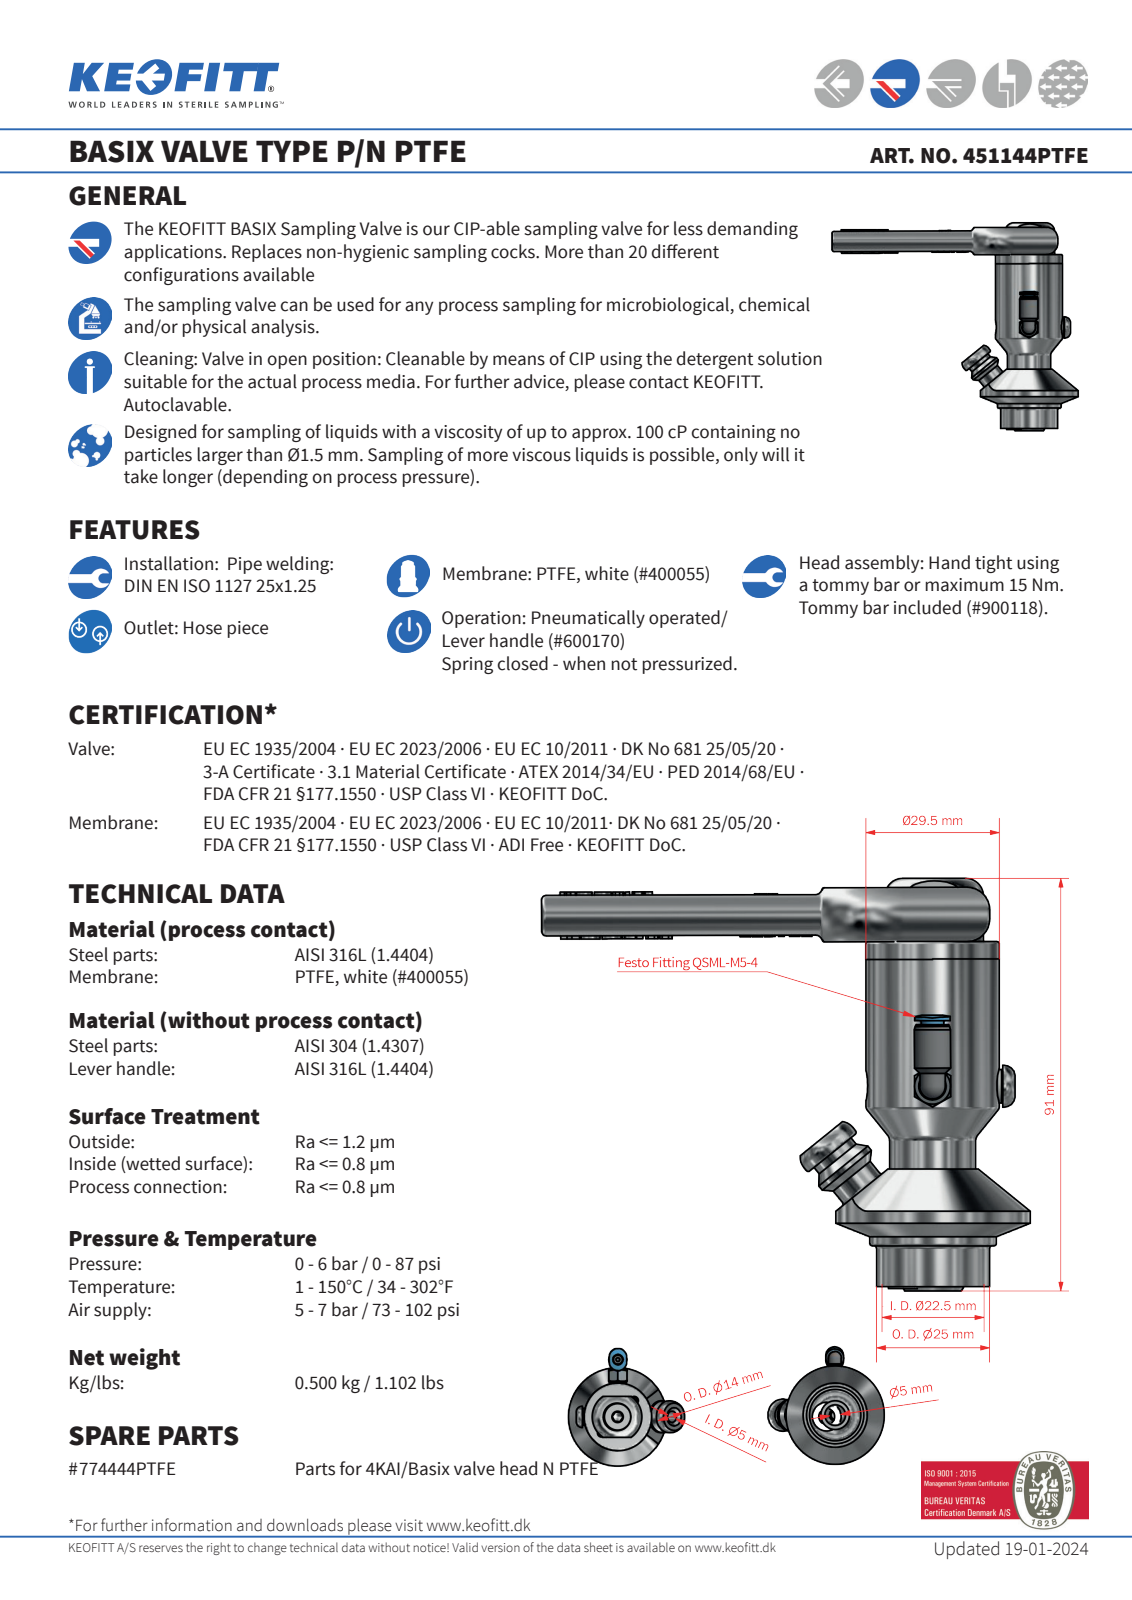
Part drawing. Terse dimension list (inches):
name: 451144PTFE
written by: Autodesk Inventor 2020 (AUTOMOTIVE_DESIGN)
unit: in
bodies: 1 solid, 776 faces (301 planar, 148 cylindrical, 327 other)
size: 4.583 × 3.61 × 2.024
volume: 3.976 in³; area: 42.13 in²
holes: 2× ⌀0.067, 2× ⌀0.118, 2× ⌀0.169, 2× ⌀0.199, 2× ⌀0.315, 1× ⌀0.157, 1× ⌀0.197, 1× ⌀0.238, 1× ⌀0.398, 1× ⌀0.476, 1× ⌀0.512, 1× ⌀0.551
bosses: 3× ⌀0.551, 3× ⌀0.197, 2× ⌀0.63, 2× ⌀0.413, 2× ⌀0.291, 2× ⌀0.26, 2× ⌀0.236, 2× ⌀0.22
rounds: 14× R0.02, 12× R0.02, 2× R0.039, 2× R0.059, 2× R0.118, 2× R0.154, 2× R0.197, 2× R0.315
face distances: 0.059, 0.413, 0.354, 0.122, 0.472, 0.748, 0.157, 1.319, 0.079, 2.114
hole spacings: 0.393, 0.394, 0.394, 0.394, 0.787
